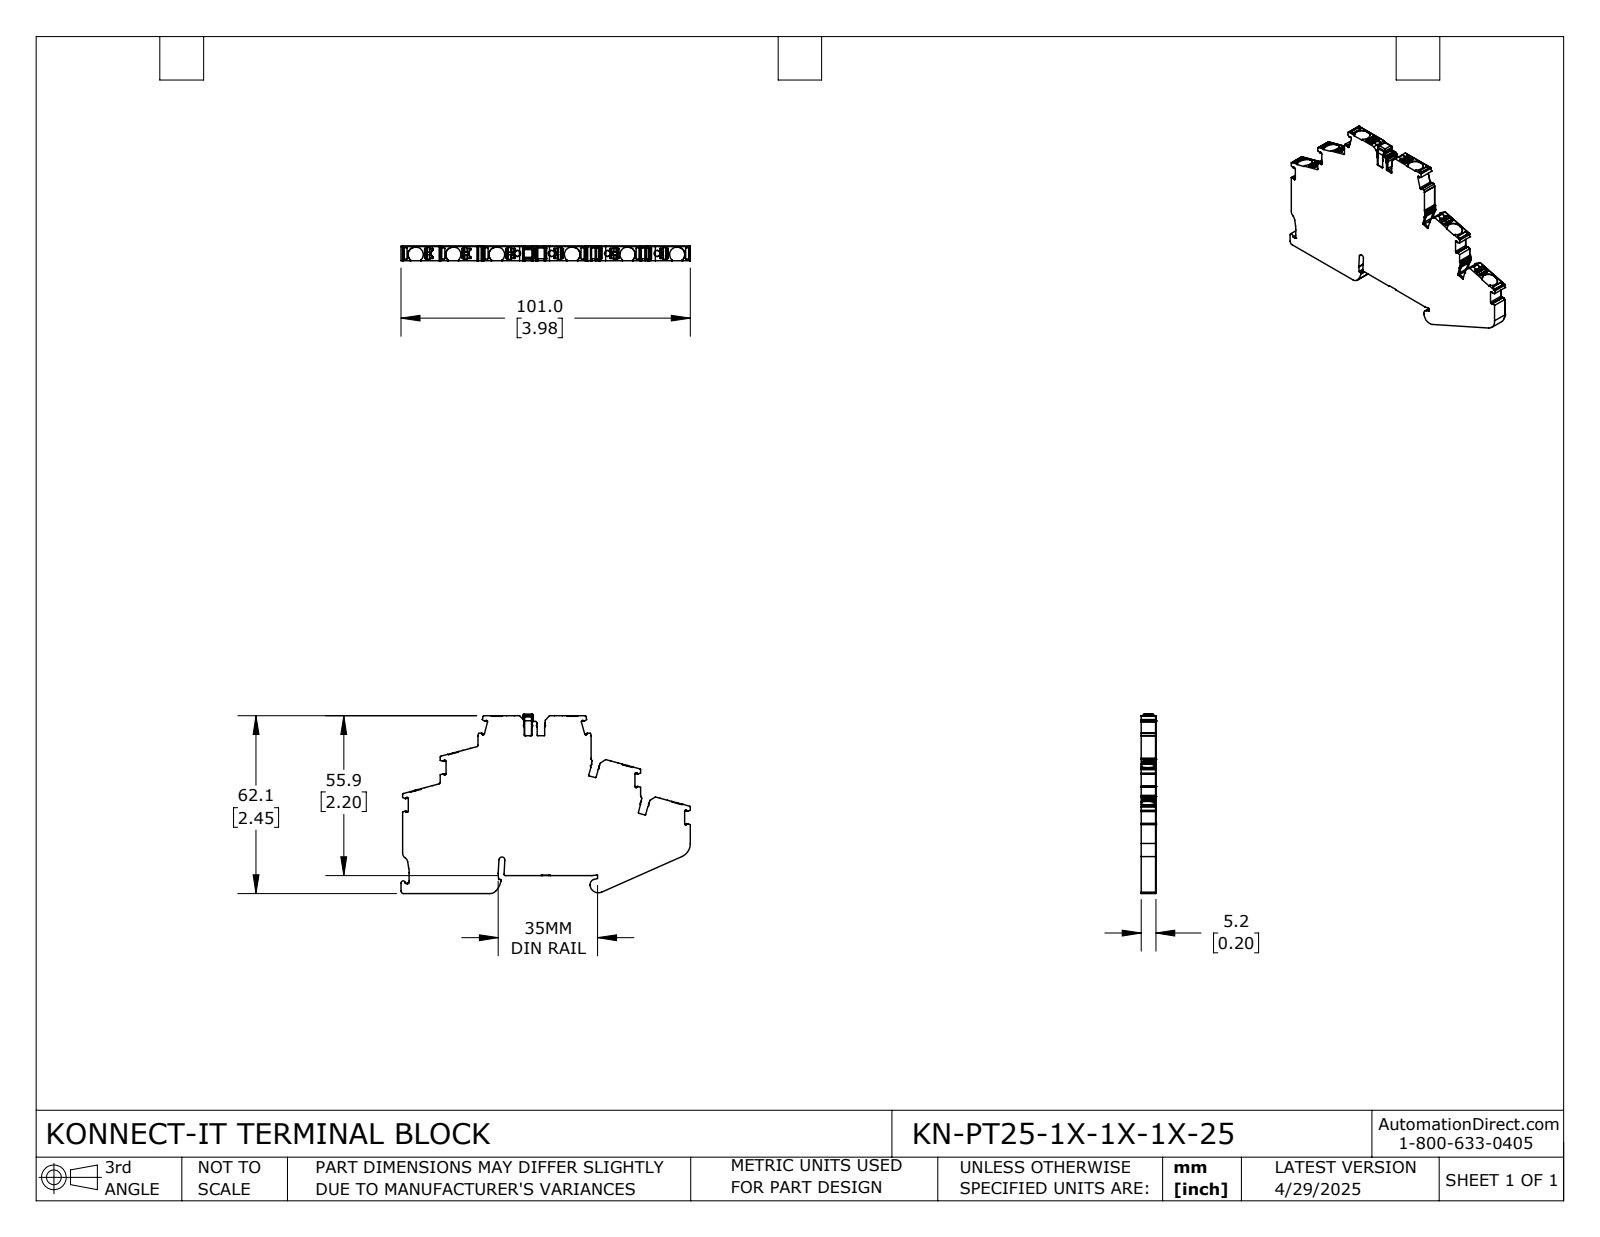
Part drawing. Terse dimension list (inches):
name: KN-PT25-1X-1X-1X-25
written by: SolidWorks 2024 (CONFIG_CONTROL_DESIGN)
unit: in
bodies: 1 solid, 1314 faces (638 planar, 565 cylindrical, 111 other)
size: 3.977 × 2.469 × 0.203
volume: 1.36 in³; area: 16.91 in²
holes: 4× ⌀0.083
rounds: 132× R0.008, 51× R0.012, 49× R0.004, 34× R0.02, 24× R0.006, 17× R0.016, 14× R0.024, 12× R0.006
face distances: 0.203, 0.246, 0.079, 2.191, 2.437, 0.319, 0.682, 0.519, 2.199, 2.445
hole spacings: 0.466, 0.792
